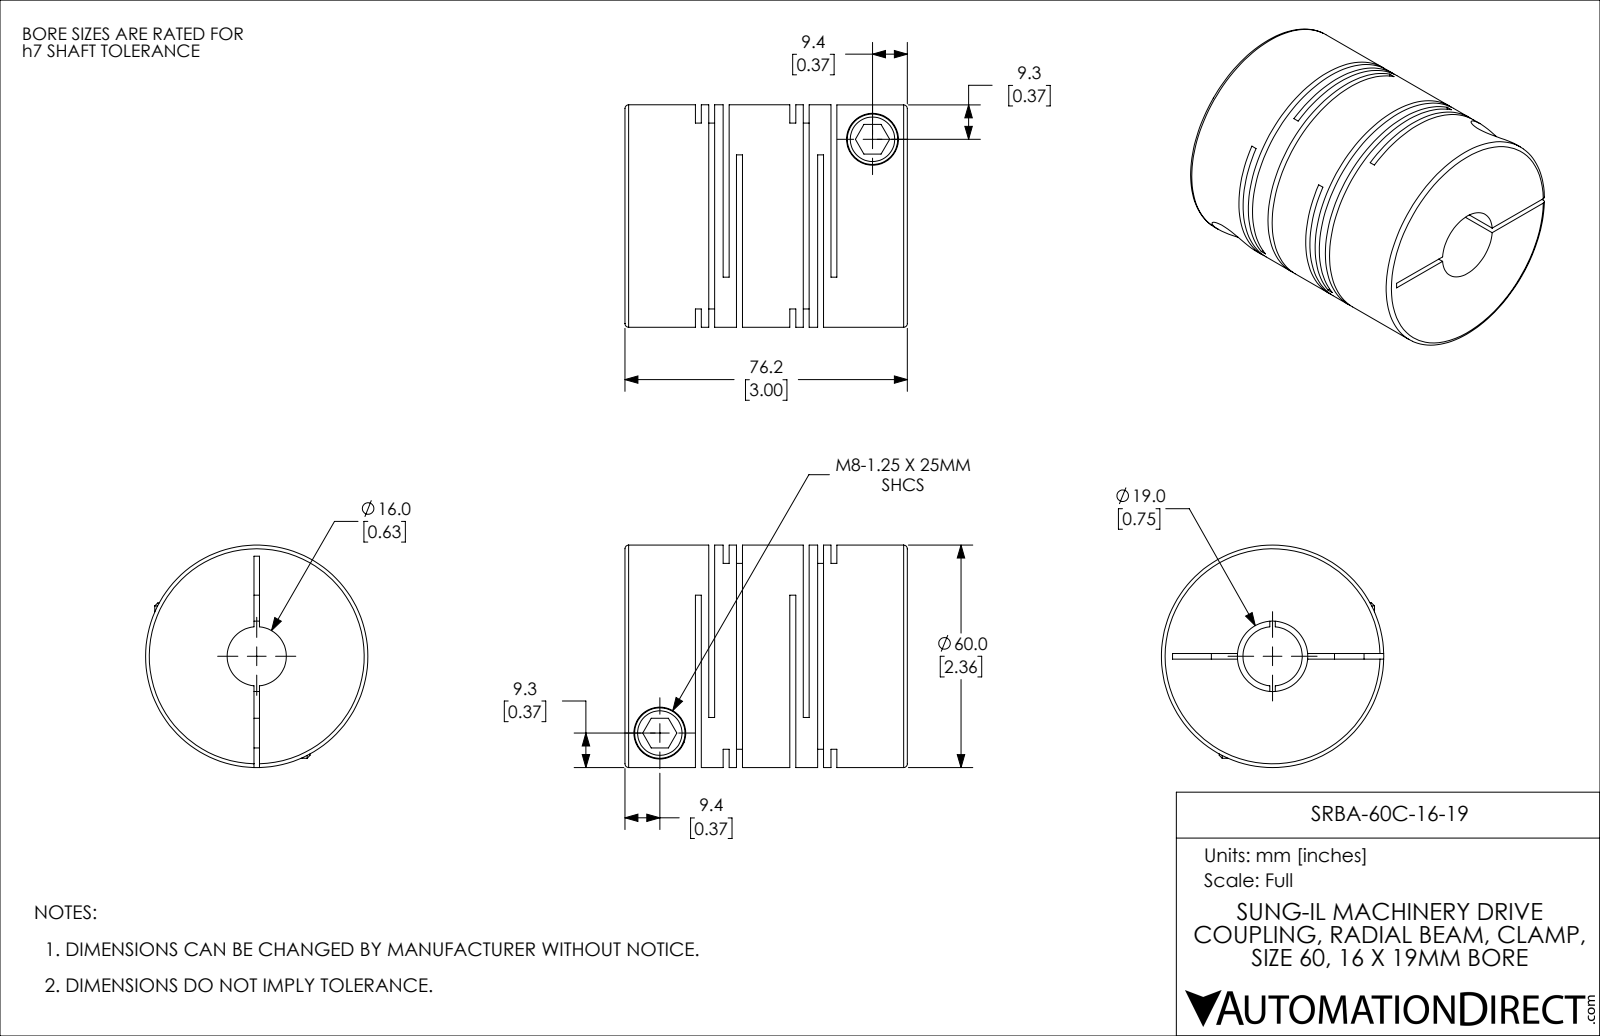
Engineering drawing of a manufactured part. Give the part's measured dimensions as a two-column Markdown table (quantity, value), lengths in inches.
| quantity | value |
| --- | --- |
| part name | SRBA-60C-16-19 |
| STEP written by | SolidWorks 2021 (CONFIG_CONTROL_DESIGN) |
| units | inches |
| bodies | 1 solid, 115 faces (60 planar, 42 cylindrical, 13 other) |
| overall size | 3 × 2.362 × 2.362 |
| volume | 9.987 in³ |
| surface area | 92.44 in² |
| round holes (diameter × count) | 0.315 × 2, 0.551 × 2, 0.63 × 1, 0.748 × 1 |
| round bosses / shafts (diameter × count) | 0.535 × 2, 2.362 × 1 |
| main face-to-face distances | 0.063, 0.142, 0.295, 1.004, 1.299, 1.067, 0.709, 0.079, 0.232, 0.941 |
